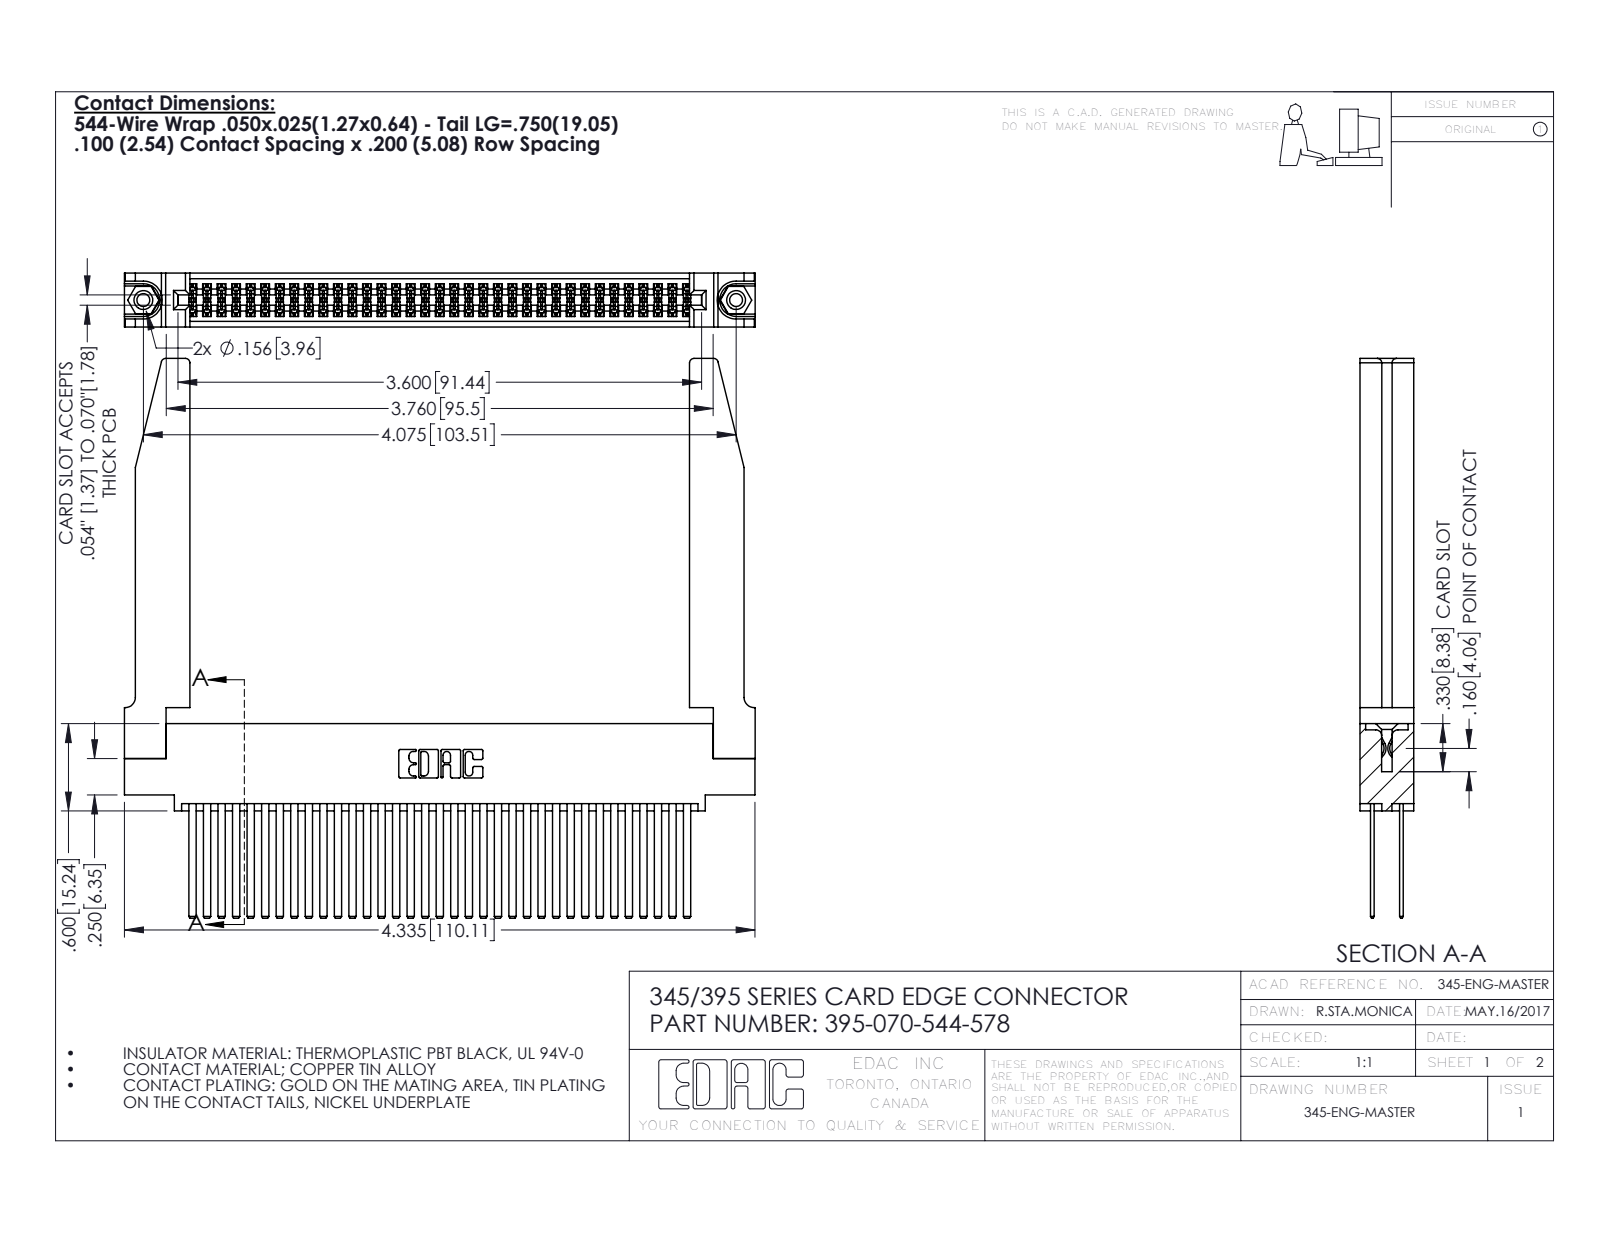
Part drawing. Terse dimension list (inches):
name: 345-220-078_345-220-078; 395-070-544-578; 345 Part_0.110 Offset - 0.156 Dia-TH; 345-250-001_345-250-001-102 (+1 more)
written by: SolidWorks 2016 (CONFIG_CONTROL_DESIGN)
unit: in
bodies: 75 solids, 3444 faces (2256 planar, 1136 cylindrical, 52 other)
size: 4.336 × 3.847 × 0.37
volume: 1.178 in³; area: 41.43 in²
holes: 2× ⌀0.089, 2× ⌀0.125, 2× ⌀0.156, 1× ⌀0.064
bosses: 2× ⌀0.155
rounds: 105× R0.006, 22× R0.01, 8× R0.03, 6× R0.007, 6× R0.031, 3× R0.026, 2× R0.014, 2× R0.019
face distances: 0.072, 0.298, 0.098, 0.272, 0.025, 0.2, 0.37, 0.225, 0.175, 0.148
hole spacings: 0.27, 3.839, 4.075
